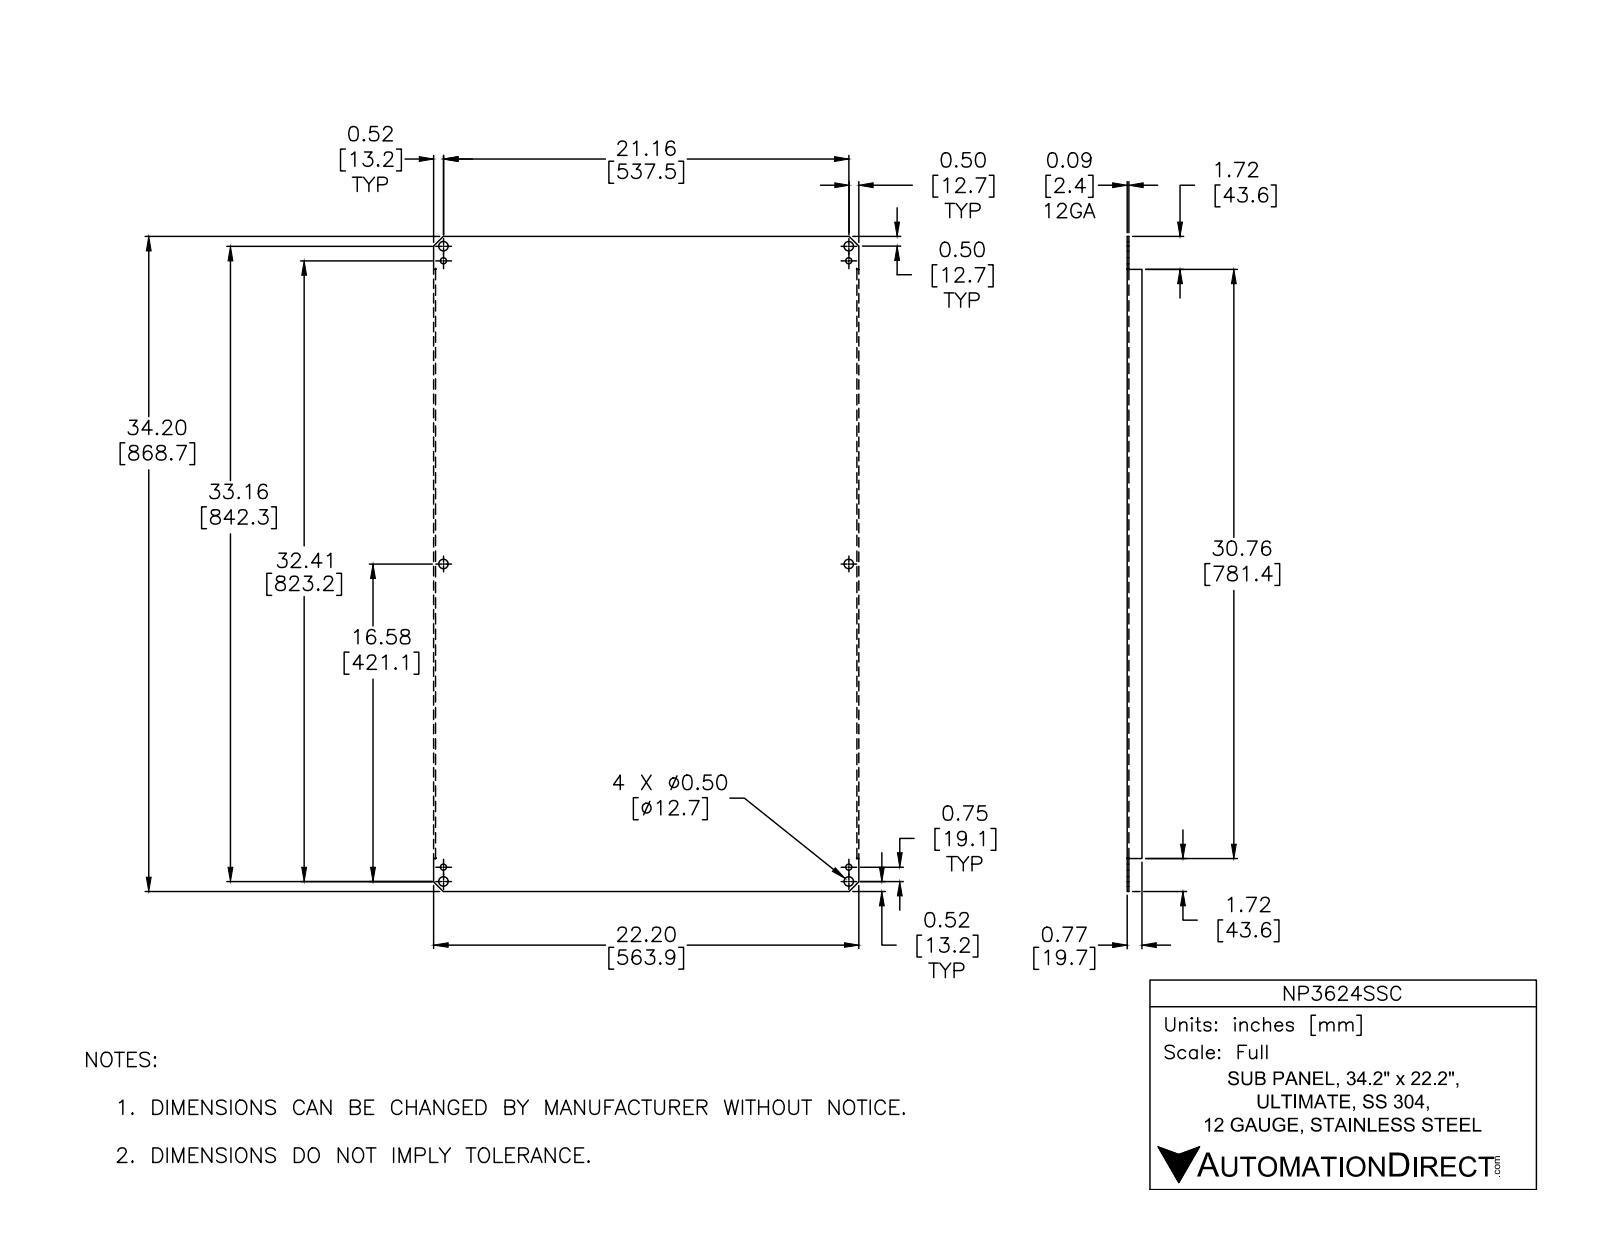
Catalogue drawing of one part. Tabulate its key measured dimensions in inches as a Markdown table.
| quantity | value |
| --- | --- |
| part name | NP3624SSC |
| STEP written by | Autodesk Inventor 2012 (AUTOMOTIVE_DESIGN) |
| units | inches |
| bodies | 1 solid, 44 faces (30 planar, 14 cylindrical, 0 other) |
| overall size | 34.2 × 22.2 × 0.774 |
| volume | 74.57 in³ |
| surface area | 1 603 in² |
| round holes (diameter × count) | 0.5 × 6, 0.313 × 4 |
| partial cylindrical surfaces (radius × count) | 0.094 × 2, 0.188 × 2 |
| main face-to-face distances | 0.094, 22.106, 22.2, 22.013, 0.68, 0.774, 34.2, 1.718, 32.482, 30.764 |
| hole center spacings | 21.16, 0.75, 15.83, 16.58, 21.173, 26.426, 26.882, 32.41 |
